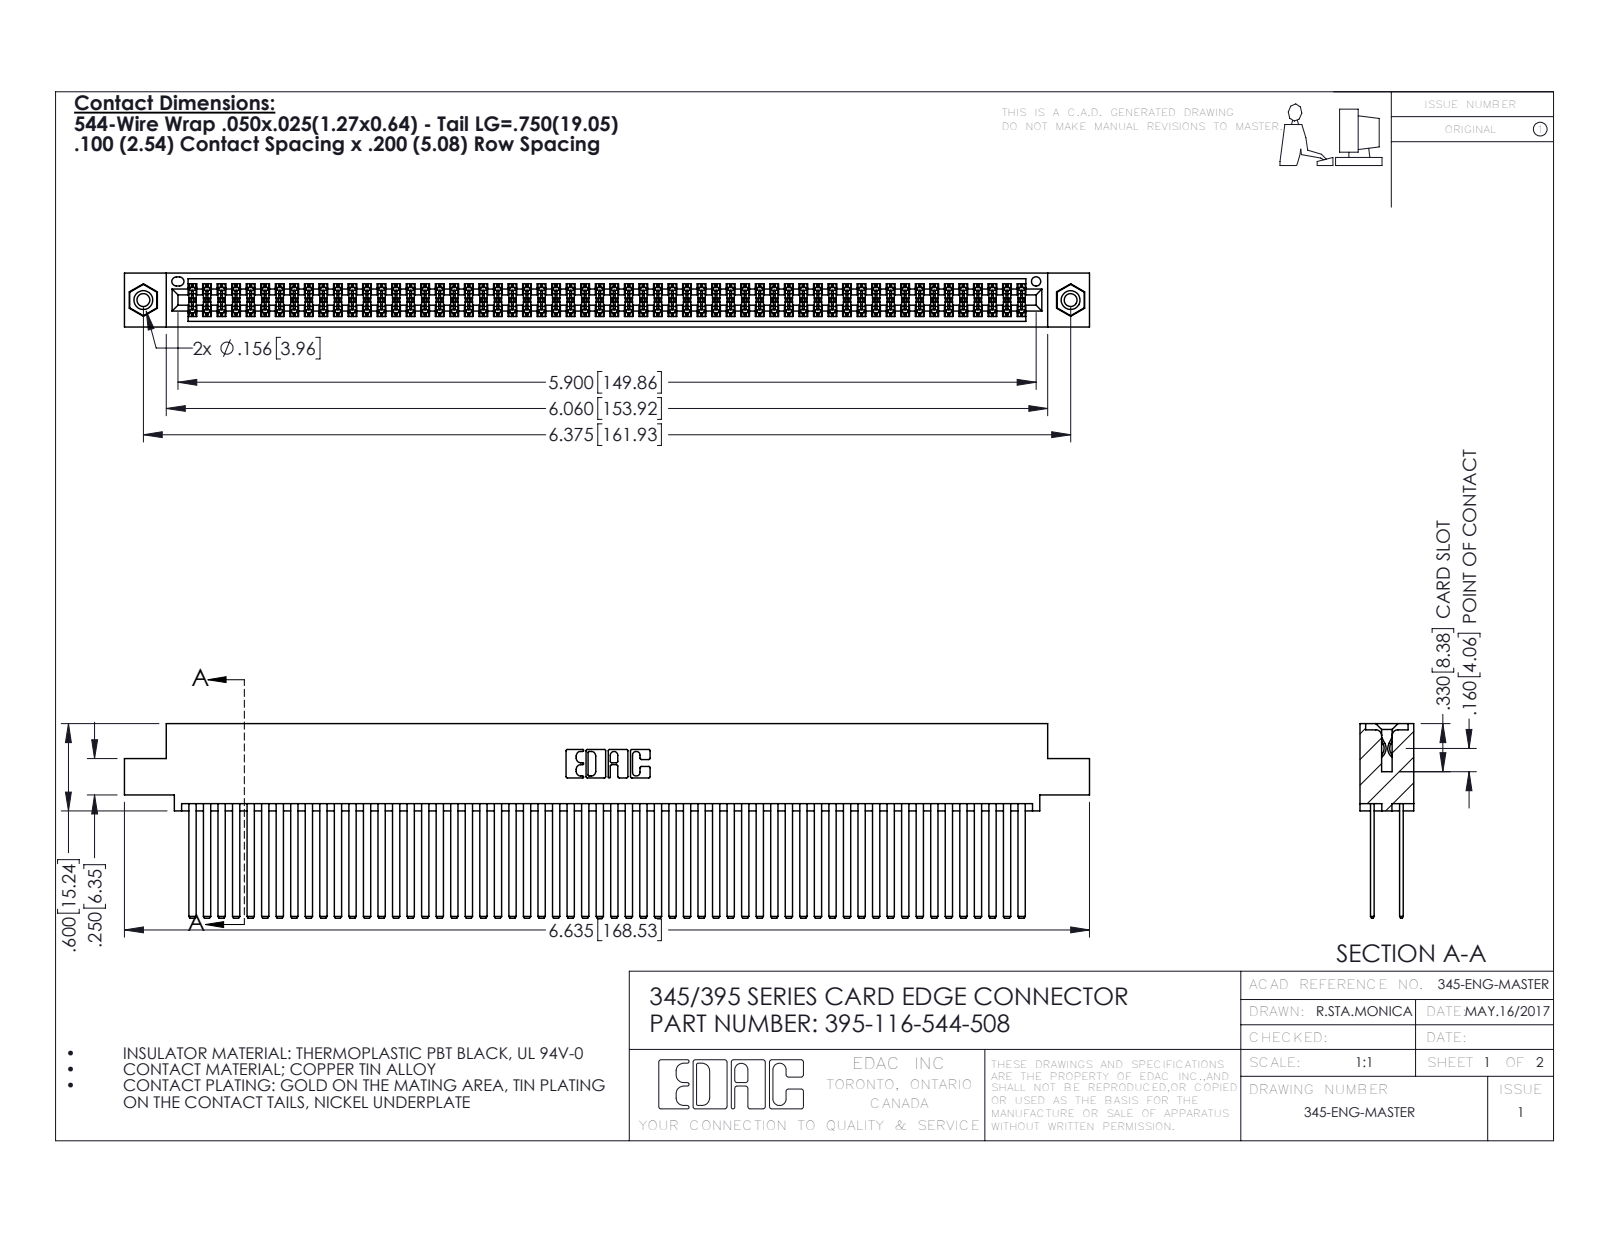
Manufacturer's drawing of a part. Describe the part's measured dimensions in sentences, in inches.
The part is named "345-292-001_345-293-144; 345-250-001_345-250-003-102; 395-116-544-508; 345 Part_0.110 Offset - 0.156 Dia-TI". Its 3-D file was written by "SolidWorks 2016 (CONFIG_CONTROL_DESIGN)". It is 119 solids with 5294 faces: 3480 planar, 1798 cylindrical and 16 other. Overall it measures 6.635 by 1.337 by 0.37 inches. Its volume is 1.102 cubic inches and its surface area 49.42 square inches. Round holes: 2 of diameter 0.089, 2 of diameter 0.125, 2 of diameter 0.156, 1 of diameter 0.064. Round bosses or shafts: 2 of diameter 0.155. Partial cylindrical surfaces (rounded edges, fillets, slot ends): 174 of radius 0.006, 22 of radius 0.01, 6 of radius 0.007, 6 of radius 0.031, 3 of radius 0.026, 2 of radius 0.014, 2 of radius 0.019, 2 of radius 0.022. The main face-to-face distances are 0.2, 0.025, 0.072, 0.098, 0.272, 0.298, 0.225, 0.175, 0.37, 0.05. The hole center spacings are 0.27, 6.139, 6.375.
